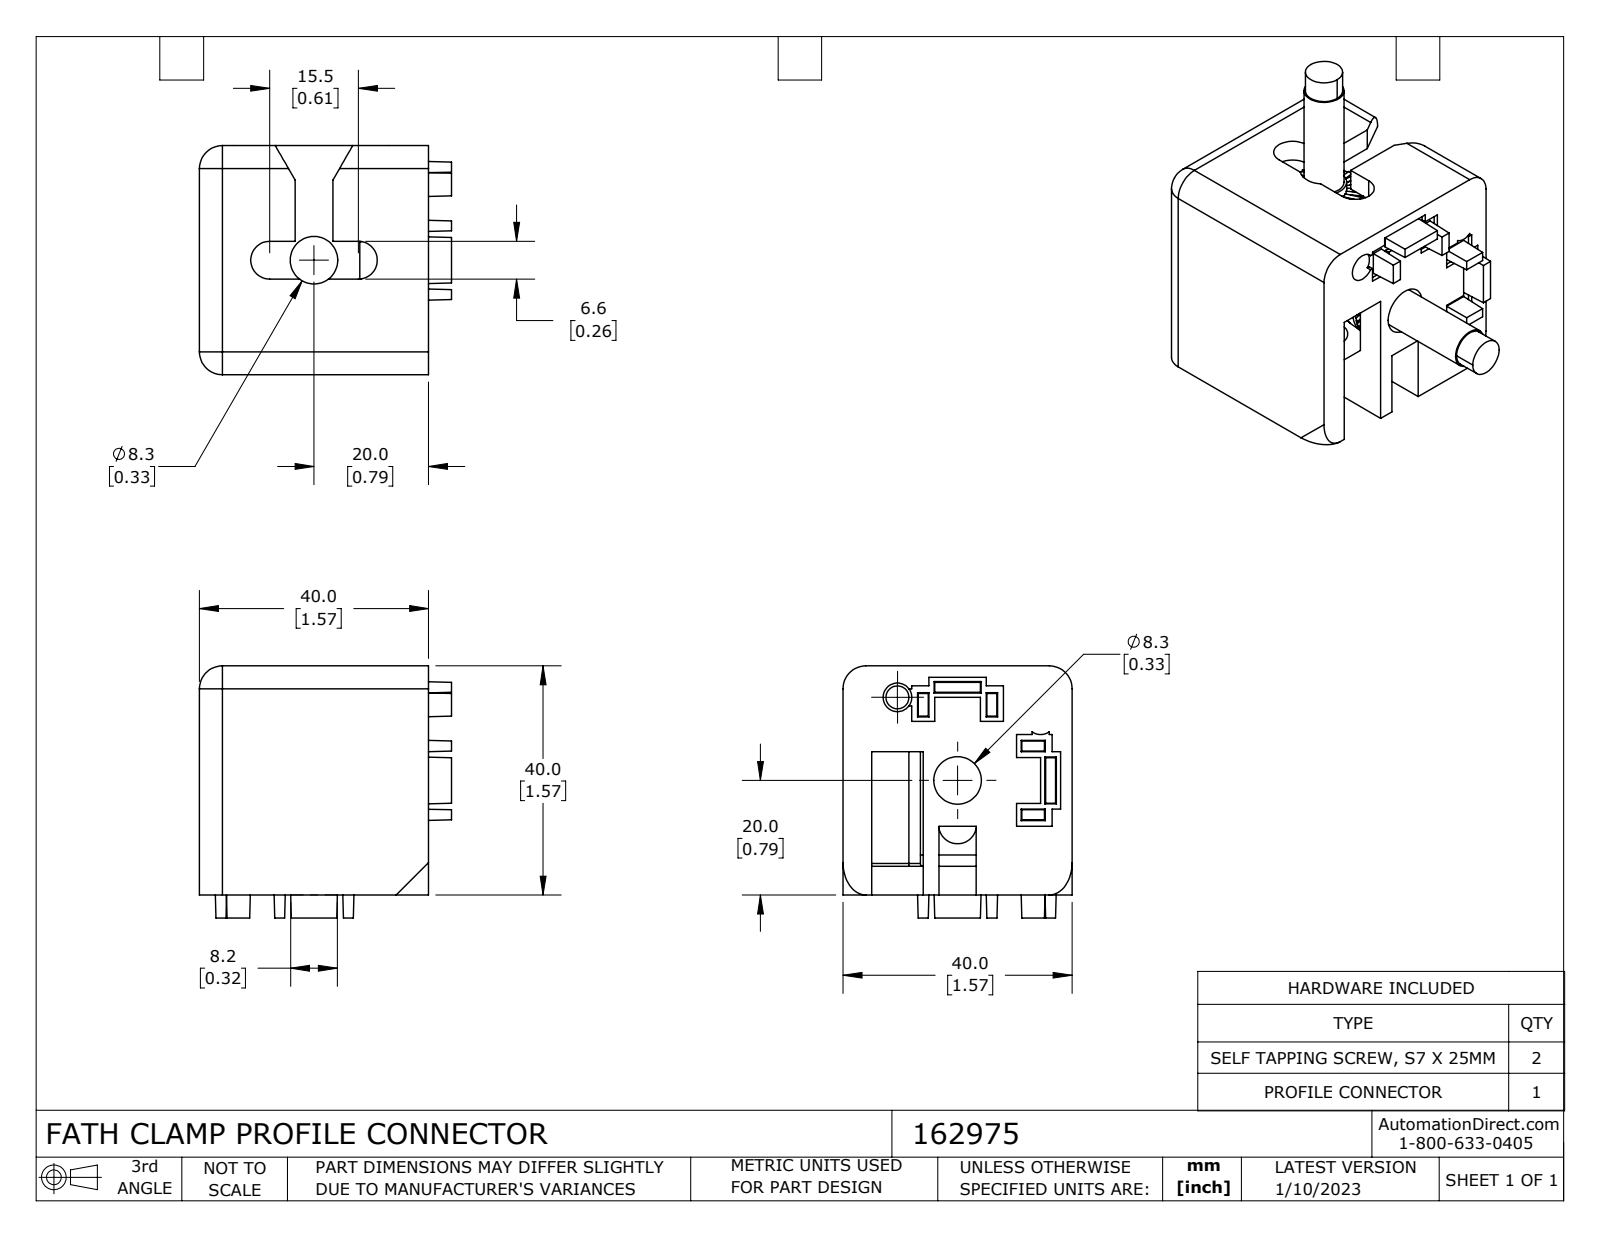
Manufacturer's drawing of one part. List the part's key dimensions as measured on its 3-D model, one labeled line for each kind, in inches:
Part name (STEP PRODUCT): 162975
STEP written by: SolidWorks 2023 (CONFIG_CONTROL_DESIGN)
Units: inches
Bodies: 3 solids, 453 faces (374 planar, 55 cylindrical, 24 other)
Overall size (bounding box): 2.362 × 2.362 × 1.575
Volume: 1.87 in³ · Surface area: 25.66 in²
Round holes (diameter × count): ⌀0.197 ×2, ⌀0.327 ×2
Round bosses / shafts (diameter × count): ⌀0.543 ×2, ⌀0.311 ×2, ⌀0.276 ×2, ⌀0.256 ×2
Partial cylindrical surfaces — rounded edges, fillets, slot ends (radius × count): R0.02 ×7, R0.157 ×7, R0.079 ×5, R0.13 ×4, R0.098 ×1
Main face-to-face distances: 1.575, 0.197, 1.378, 0.157, 1.22, 1.417, 0.276, 0.945, 0.433, 1.142
Hole centre spacings: 0.705
